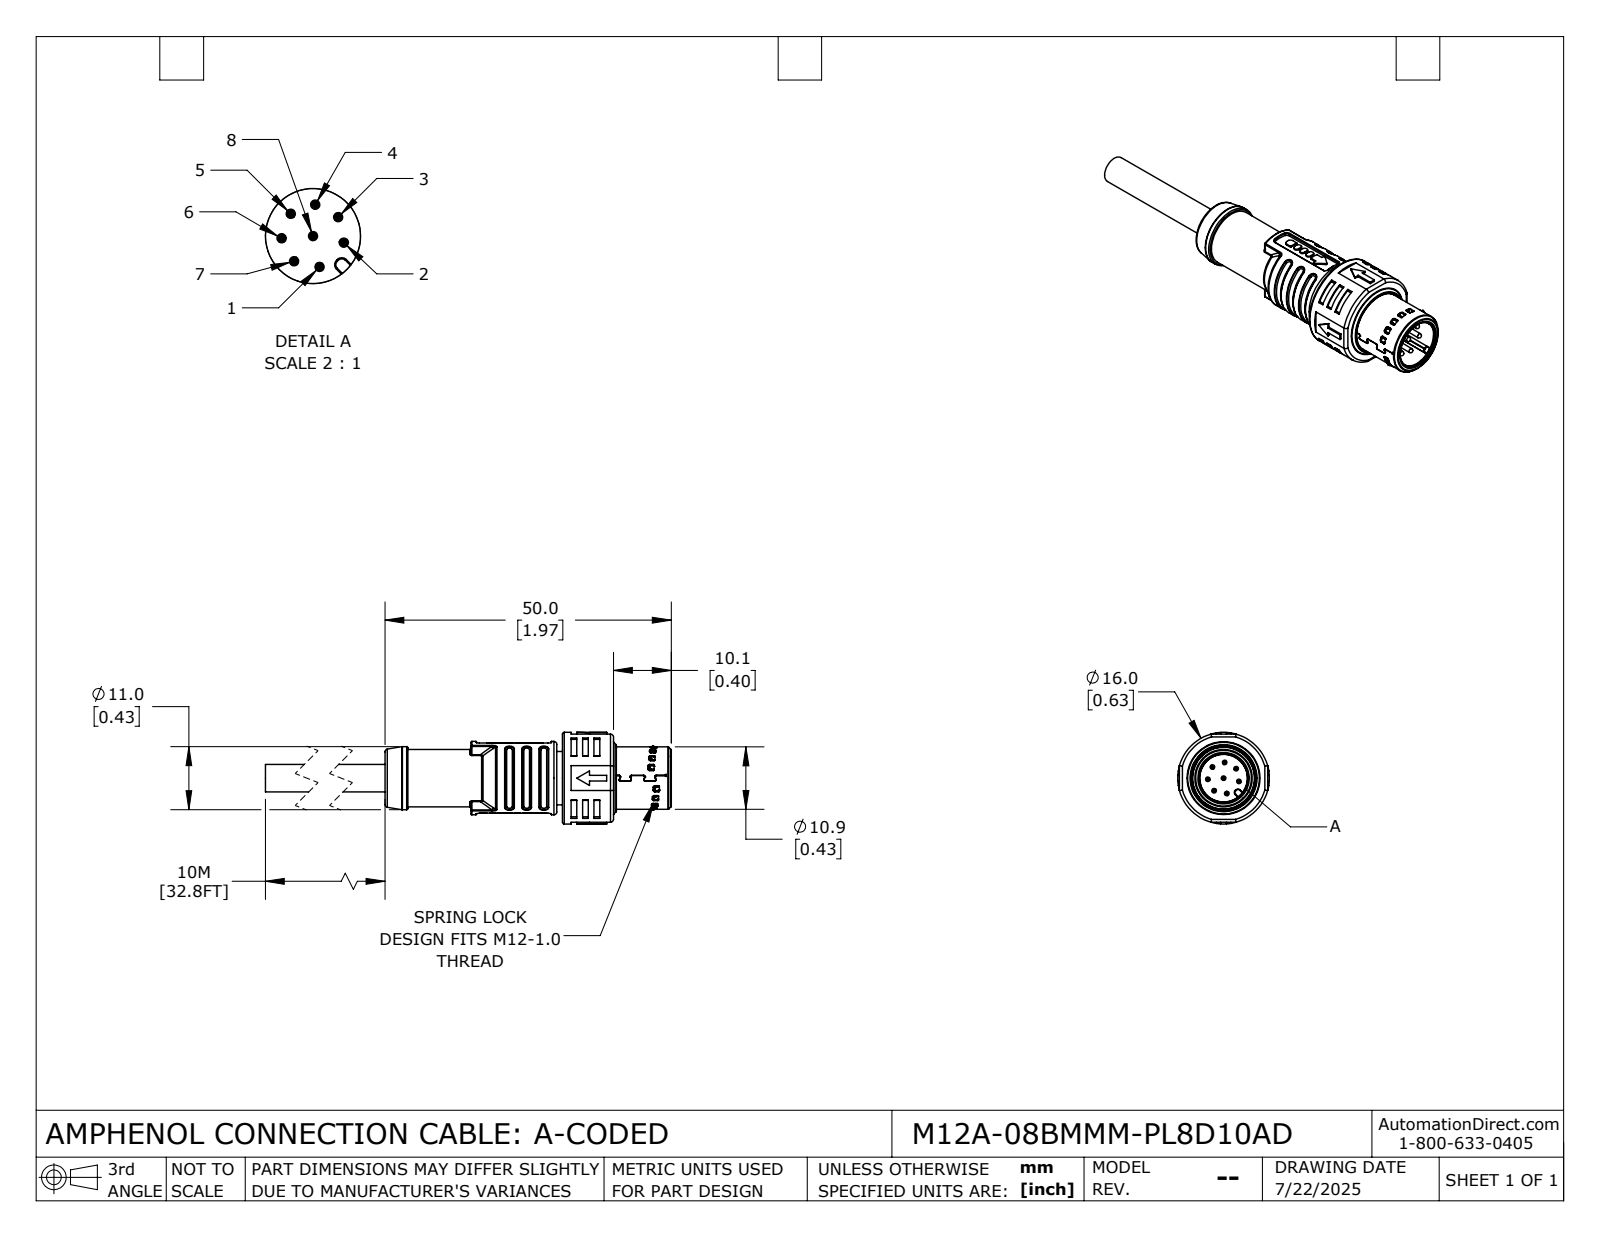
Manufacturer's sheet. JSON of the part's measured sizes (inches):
{"part_name": "M12A-08BMMM-PL8D10AD", "step_written_by": "SolidWorks 2024 (CONFIG_CONTROL_DESIGN)", "units": "inches", "bodies": {"solids": 1, "faces": 2027, "planar": 880, "cylindrical": 644, "other": 503}, "overall_size": [2.953, 0.63, 0.63], "volume_in3": 0.319, "surface_area_in2": 8.871, "round_holes": [[0.327, 1], [0.354, 1], [0.4, 1], [0.413, 1], [0.429, 1], [0.453, 1], [0.465, 1], [0.559, 1]], "round_bosses_or_shafts": [[0.031, 8], [0.63, 1], [0.555, 1], [0.504, 1], [0.488, 1], [0.433, 1], [0.411, 1], [0.409, 1]], "partial_cylinders_radius": [[0.008, 114], [0.01, 66], [0.012, 64], [0.006, 44], [0.02, 38], [0.005, 12], [0.028, 11], [0.004, 10]], "face_to_face_distances": [0.039, 0.398, 0.339, 0.35, 0.098, 0.059, 0.047, 1.28, 0.606, 1.618]}
